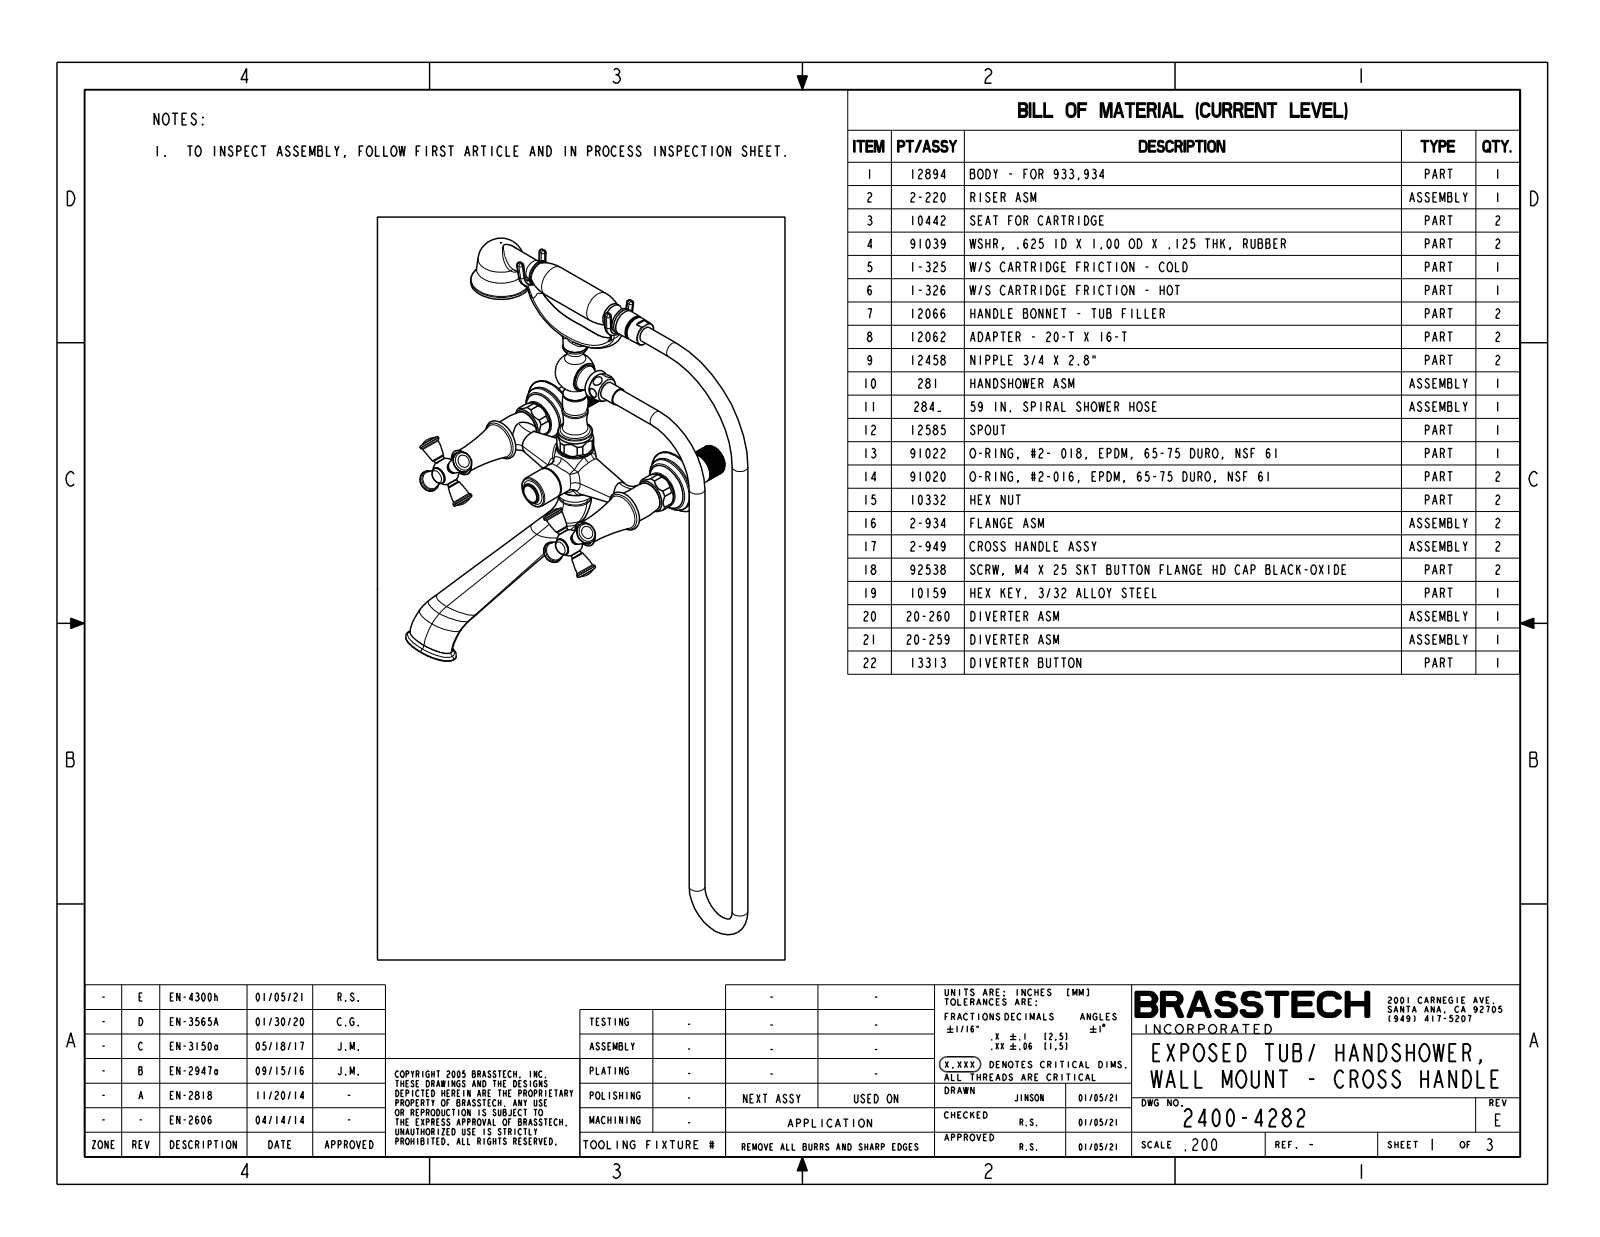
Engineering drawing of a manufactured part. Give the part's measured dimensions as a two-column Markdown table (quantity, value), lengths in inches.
| quantity | value |
| --- | --- |
| part name | 2400-4282 |
| STEP written by | CREO PARAMETRIC BY PTC INC, 2018400 (CONFIG_CONTROL_DESIGN) |
| units | inches |
| bodies | 1 solid, 961 faces (143 planar, 263 cylindrical, 555 other) |
| overall size | 23.86 × 13.181 × 9.373 |
| volume | 51.29 in³ |
| surface area | 271.5 in² |
| round holes (diameter × count) | 0.046 × 52 |
| round bosses / shafts (diameter × count) | 0.72 × 8, 0.36 × 8, 0.82 × 4, 0.54 × 4, 0.9 × 2, 0.65 × 2, 0.56 × 2, 0.517 × 2 |
| partial cylindrical surfaces (radius × count) | 0.085 × 32, 0.637 × 3, 0.595 × 2, 0.405 × 1, 0.406 × 1, 0.45 × 1 |
| main face-to-face distances | 1.188, 3, 2.466, 1.25, 1.216, 4.188, 1.812, 10.058, 5.461, 4.597 |
| hole center spacings | 0.187, 0.367, 0.535, 0.813, 1.021, 0.184, 0.601, 0.685 |
